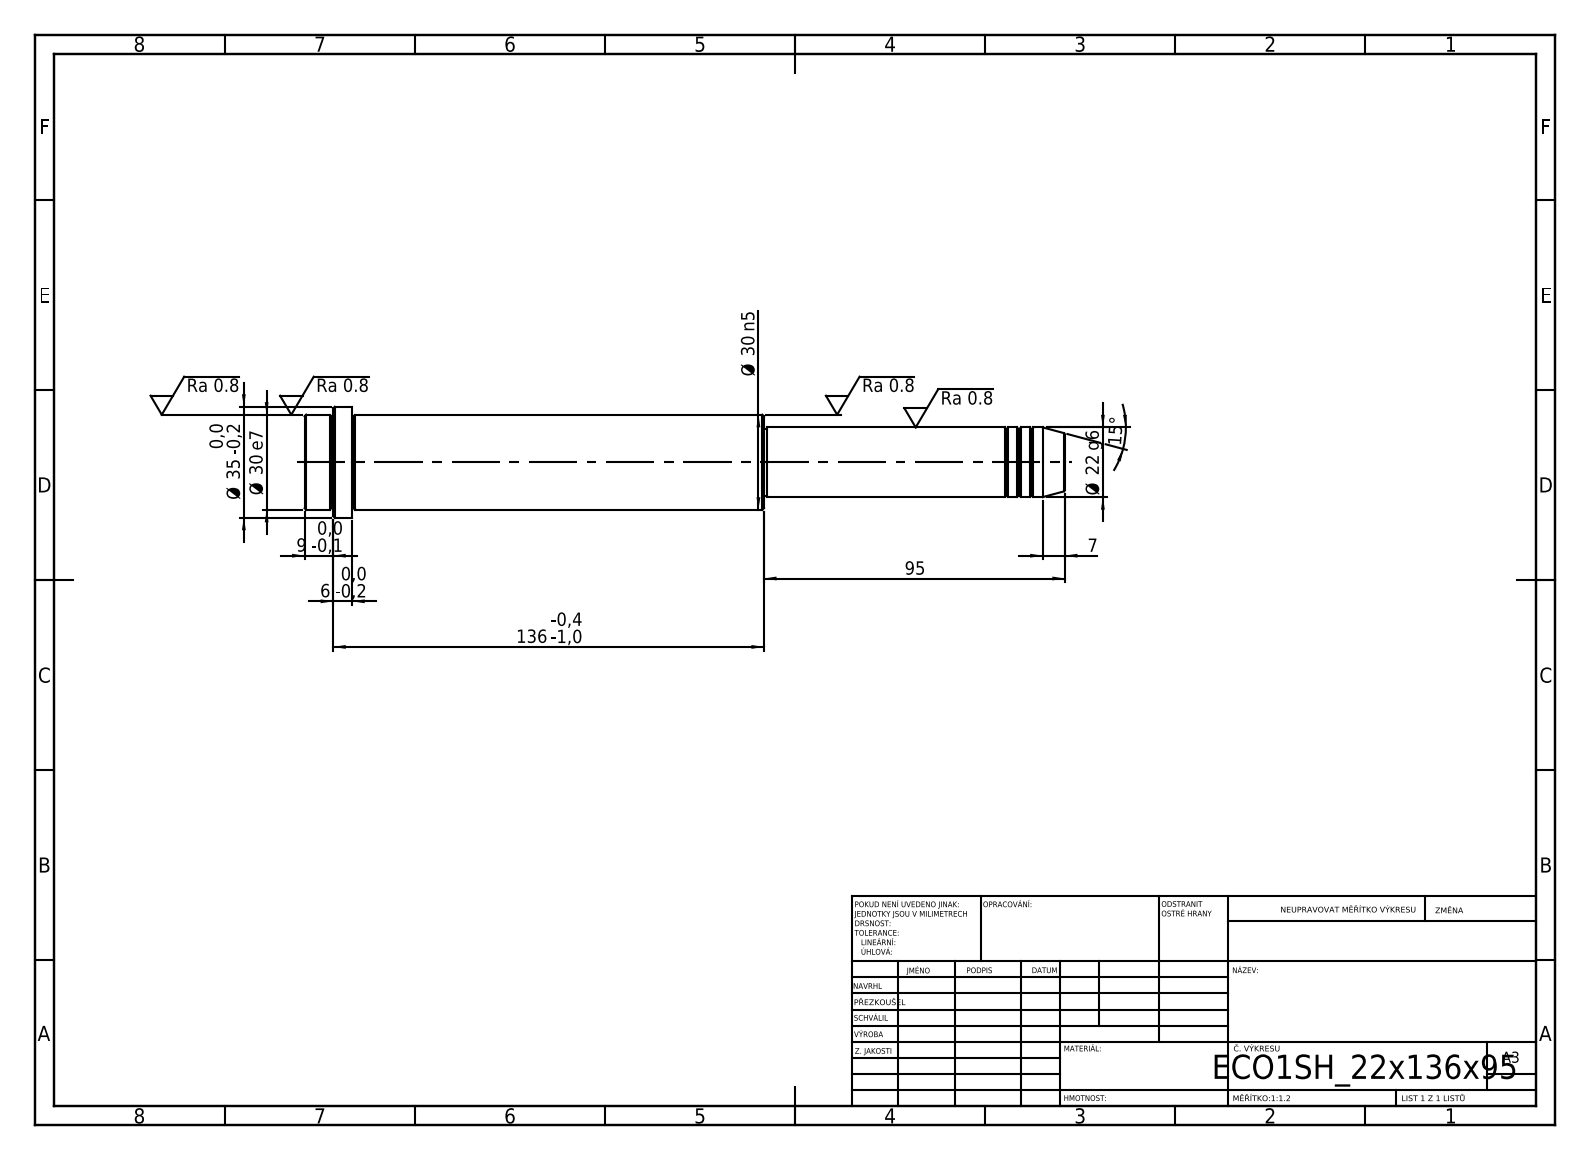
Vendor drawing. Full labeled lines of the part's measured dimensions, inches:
STEP written by: SolidWorks 2019 (CONFIG_CONTROL_DESIGN)
Units: inches
Bodies: 1 solid, 52 faces (6 planar, 16 cylindrical, 30 other)
Overall size (bounding box): 9.449 × 1.378 × 1.378
Volume: 8.512 in³ · Surface area: 34.54 in²
Round bosses / shafts (diameter × count): ⌀1.378 ×1, ⌀1.181 ×1, ⌀0.866 ×1, ⌀0.827 ×1
Main face-to-face distances: 5.709, 5.118, 0.591, 3.74, 8.858, 9.449, 9.094, 5.354, 0.236, 0.354
